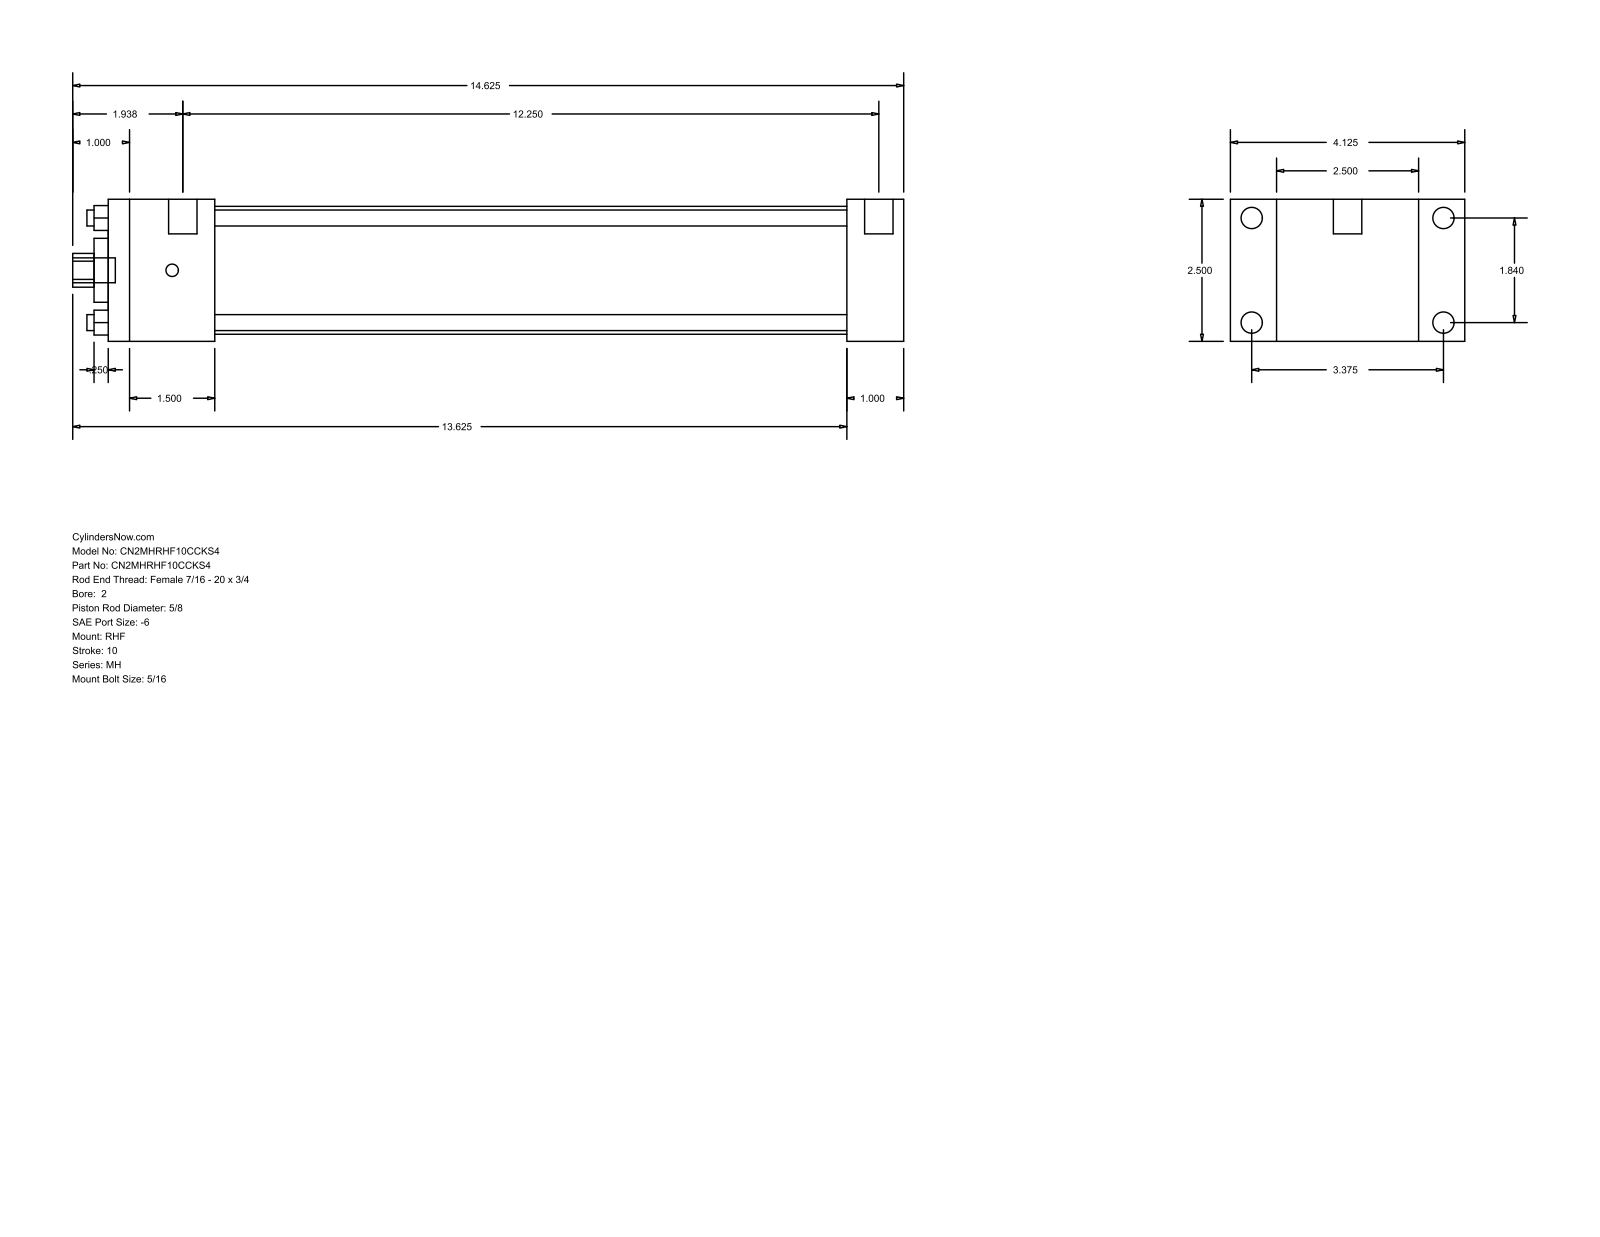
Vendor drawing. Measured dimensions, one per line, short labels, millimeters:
name: MH_RHF__0200_0.625
written by: GSSL Pune (CONFIG_CONTROL_DESIGN)
unit: mm
bodies: 0 solids, 88 faces (60 planar, 28 cylindrical, 0 other)
size: 371.48 × 104.78 × 63.5
holes: 4× ⌀7.14, 1× ⌀15.88, 1× ⌀28.57, 1× ⌀57.15
bosses: 4× ⌀9.53, 4× ⌀5.56, 2× ⌀12.7, 1× ⌀11.11
rounds: 1× R7.54
face distances: 63.5, 25.41, 20.64, 84.14, 330.19, 355.6, 104.78, 47.62, 282.57, 307.98
hole spacings: 33.05, 46.74, 66.1
